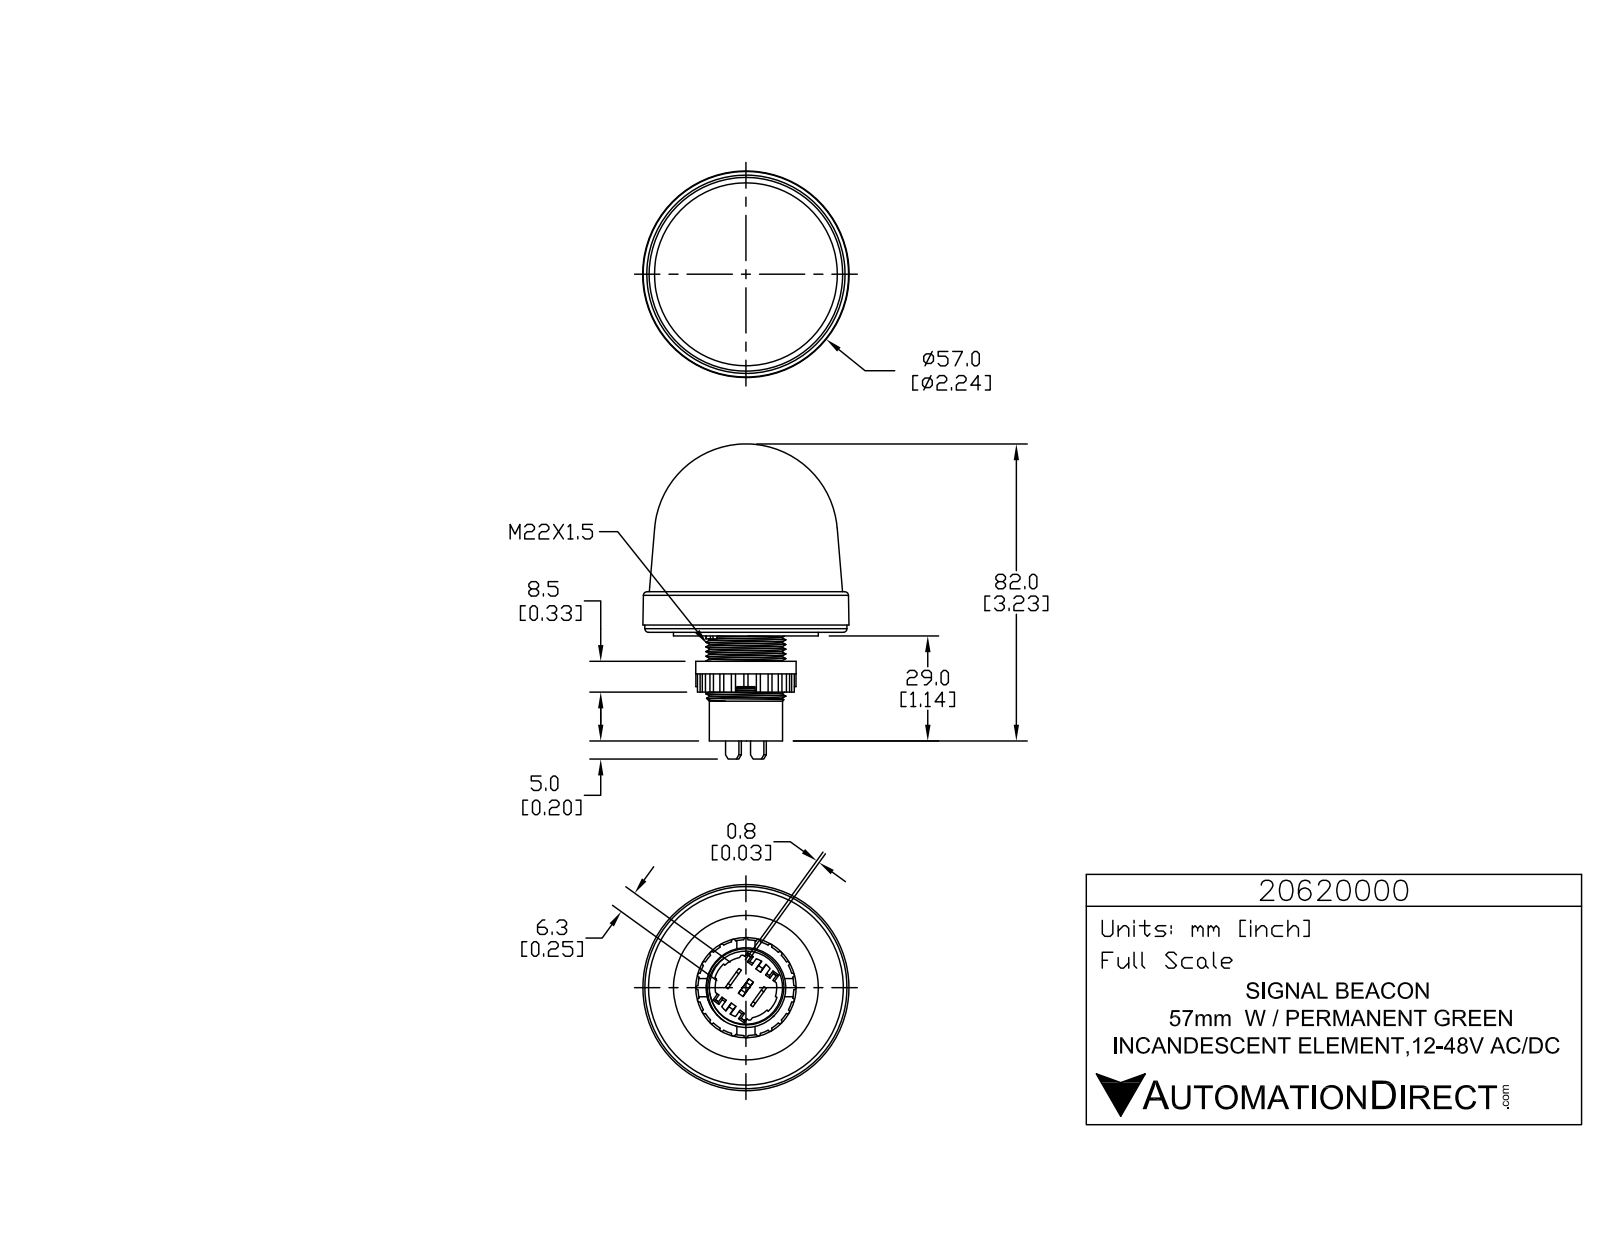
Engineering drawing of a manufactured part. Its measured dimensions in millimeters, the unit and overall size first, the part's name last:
Units: millimetres
Overall size (bounding box): 86.7 × 56.9 × 56.9
Round holes (diameter × count): ⌀1 ×3, ⌀23 ×1
Round bosses / shafts (diameter × count): ⌀5.7 ×3, ⌀1.4 ×3, ⌀55.8 ×1, ⌀40 ×1, ⌀27.7 ×1, ⌀22 ×1, ⌀20.2 ×1
Partial cylindrical surfaces — rounded edges, fillets, slot ends (radius × count): R0.6 ×24, R0.2 ×6, R0.2 ×6, R0.2 ×6, R3.3 ×6, R0.1 ×3, R0.1 ×3, R0.2 ×3
Main face-to-face distances: 1, 7, 8.5, 8, 27, 19, 26, 3, 29, 10.5
Volume: 106 200 mm³ · Surface area: 16 820 mm²
Bodies: 1 solid, 1002 faces (637 planar, 266 cylindrical, 99 other)
Part name (STEP PRODUCT): 20620000
STEP written by: SolidWorks 2015 (AUTOMOTIVE_DESIGN)
